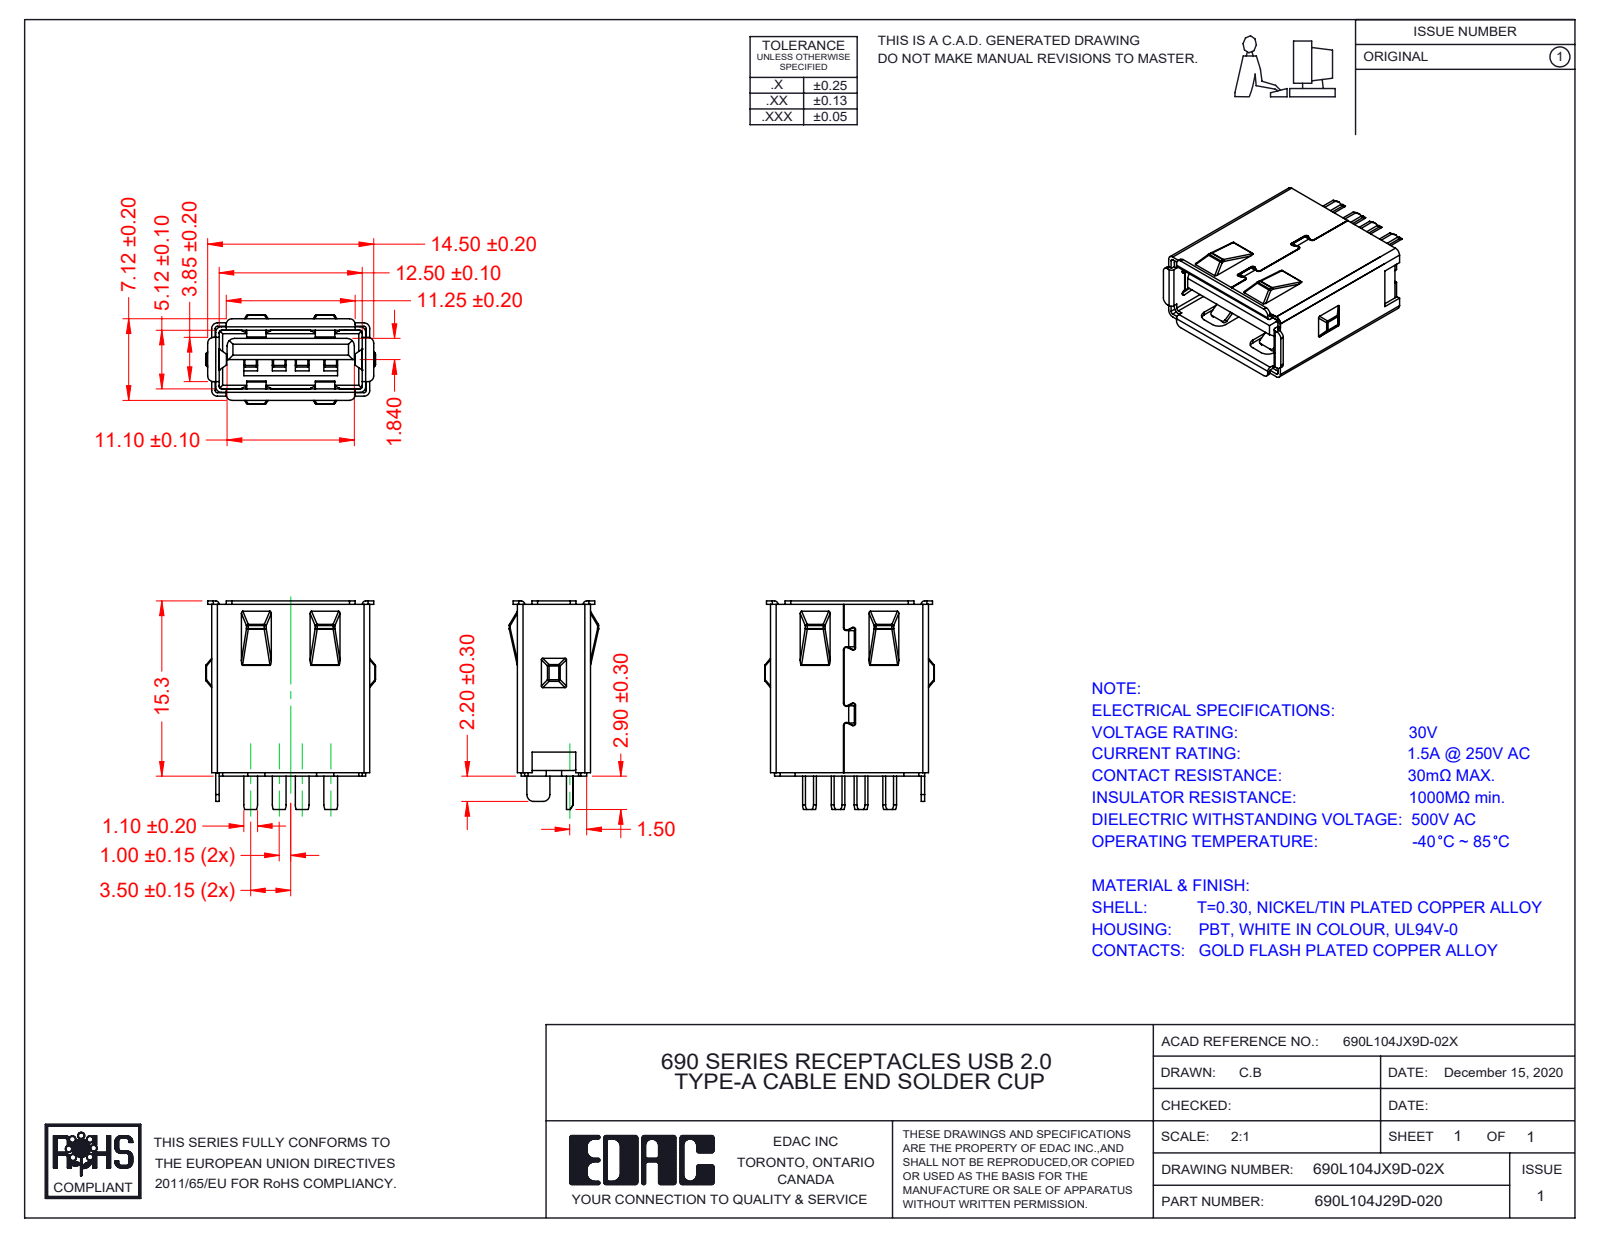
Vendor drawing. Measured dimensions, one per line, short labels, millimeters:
name: Shell 690L104JX9D-02X; Insulator 2 690L104JX9D-02X_White; Jacket 690L104JX9D-02X; Insulator 690L104JX9D-02X_White (+2 more)
written by: SolidWorks 2020 (AUTOMOTIVE_DESIGN)
unit: mm
bodies: 8 solids, 1045 faces (678 planar, 297 cylindrical, 70 other)
size: 18.2 × 14.8 × 7.8
volume: 793 mm³; area: 3 425 mm²
rounds: 81× R0.2, 35× R0.3, 31× R0.15, 19× R0.5, 17× R0.25, 4× R0.2, 4× R0.24, 4× R0.26
face distances: 0.34, 5.76, 0.35, 6.1, 0.65, 0.64, 5.46, 6.06, 5.42, 13.15
